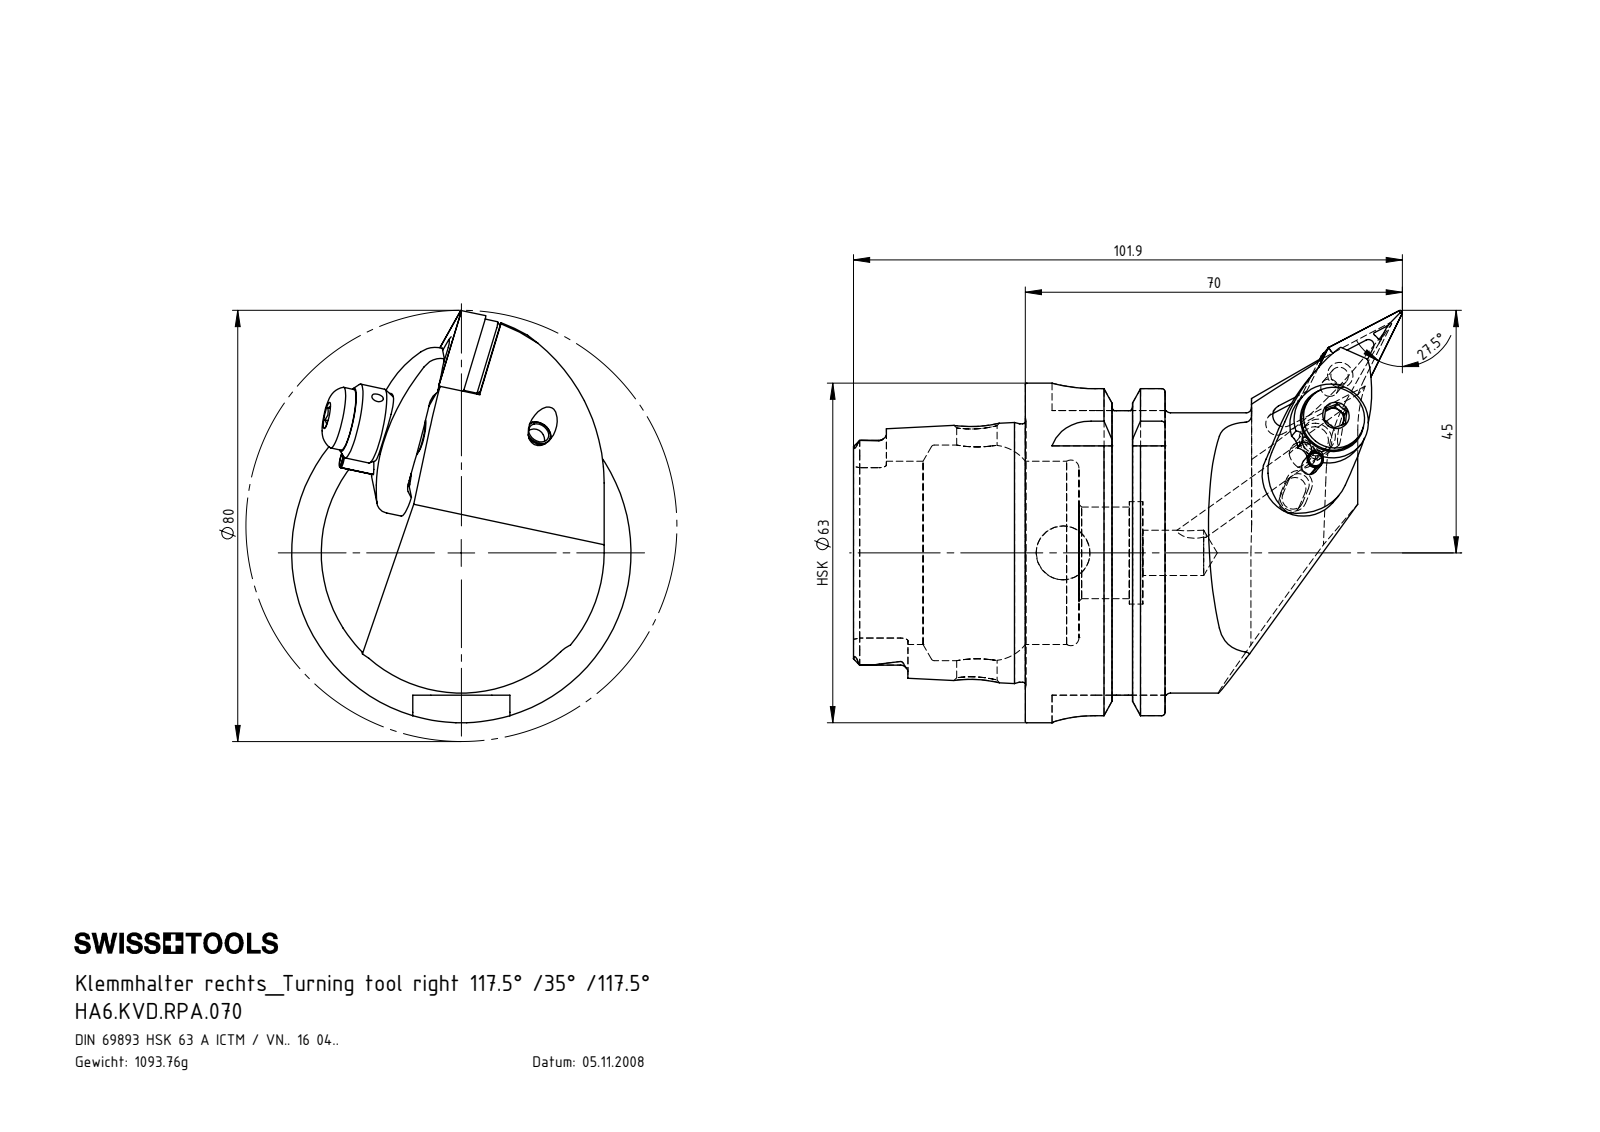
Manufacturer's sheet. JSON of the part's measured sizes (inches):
{"part_name": "HA6-KVD.RPA.070_E; VNMG160404; WCC-ER2.001.010_A; KVT_MB_600_050 (+7 more)", "step_written_by": "SolidWorks 2017 (AUTOMOTIVE_DESIGN)", "units": "inches", "bodies": {"solids": 11, "faces": 464, "planar": 126, "cylindrical": 153, "other": 185}, "overall_size": [4.012, 3.012, 2.48], "volume_in3": 8.47, "surface_area_in2": 52.56, "round_holes": [[0.079, 3], [0.197, 2], [0.276, 2], [0.094, 1], [0.118, 1], [0.13, 1], [0.15, 1], [0.157, 1], [0.165, 1], [0.195, 1], [0.244, 1], [0.272, 1]], "round_bosses_or_shafts": [[0.197, 2], [0.118, 2], [2.48, 1], [2.163, 1], [2.047, 1], [1.887, 1], [0.551, 1], [0.453, 1]], "partial_cylinders_radius": [[0.015, 6], [0.055, 6], [0.016, 4], [0.315, 4], [0.027, 3], [0.027, 3], [0.059, 3], [1.575, 3]], "face_to_face_distances": [1.022, 0.63, 0.392, 1.256, 1.648, 2.278, 2.079, 0.858, 0.175, 0.467], "hole_center_spacings": [0.556, 0.562, 0.563, 0.878, 0.879, 0.879, 0.315, 0.316]}
